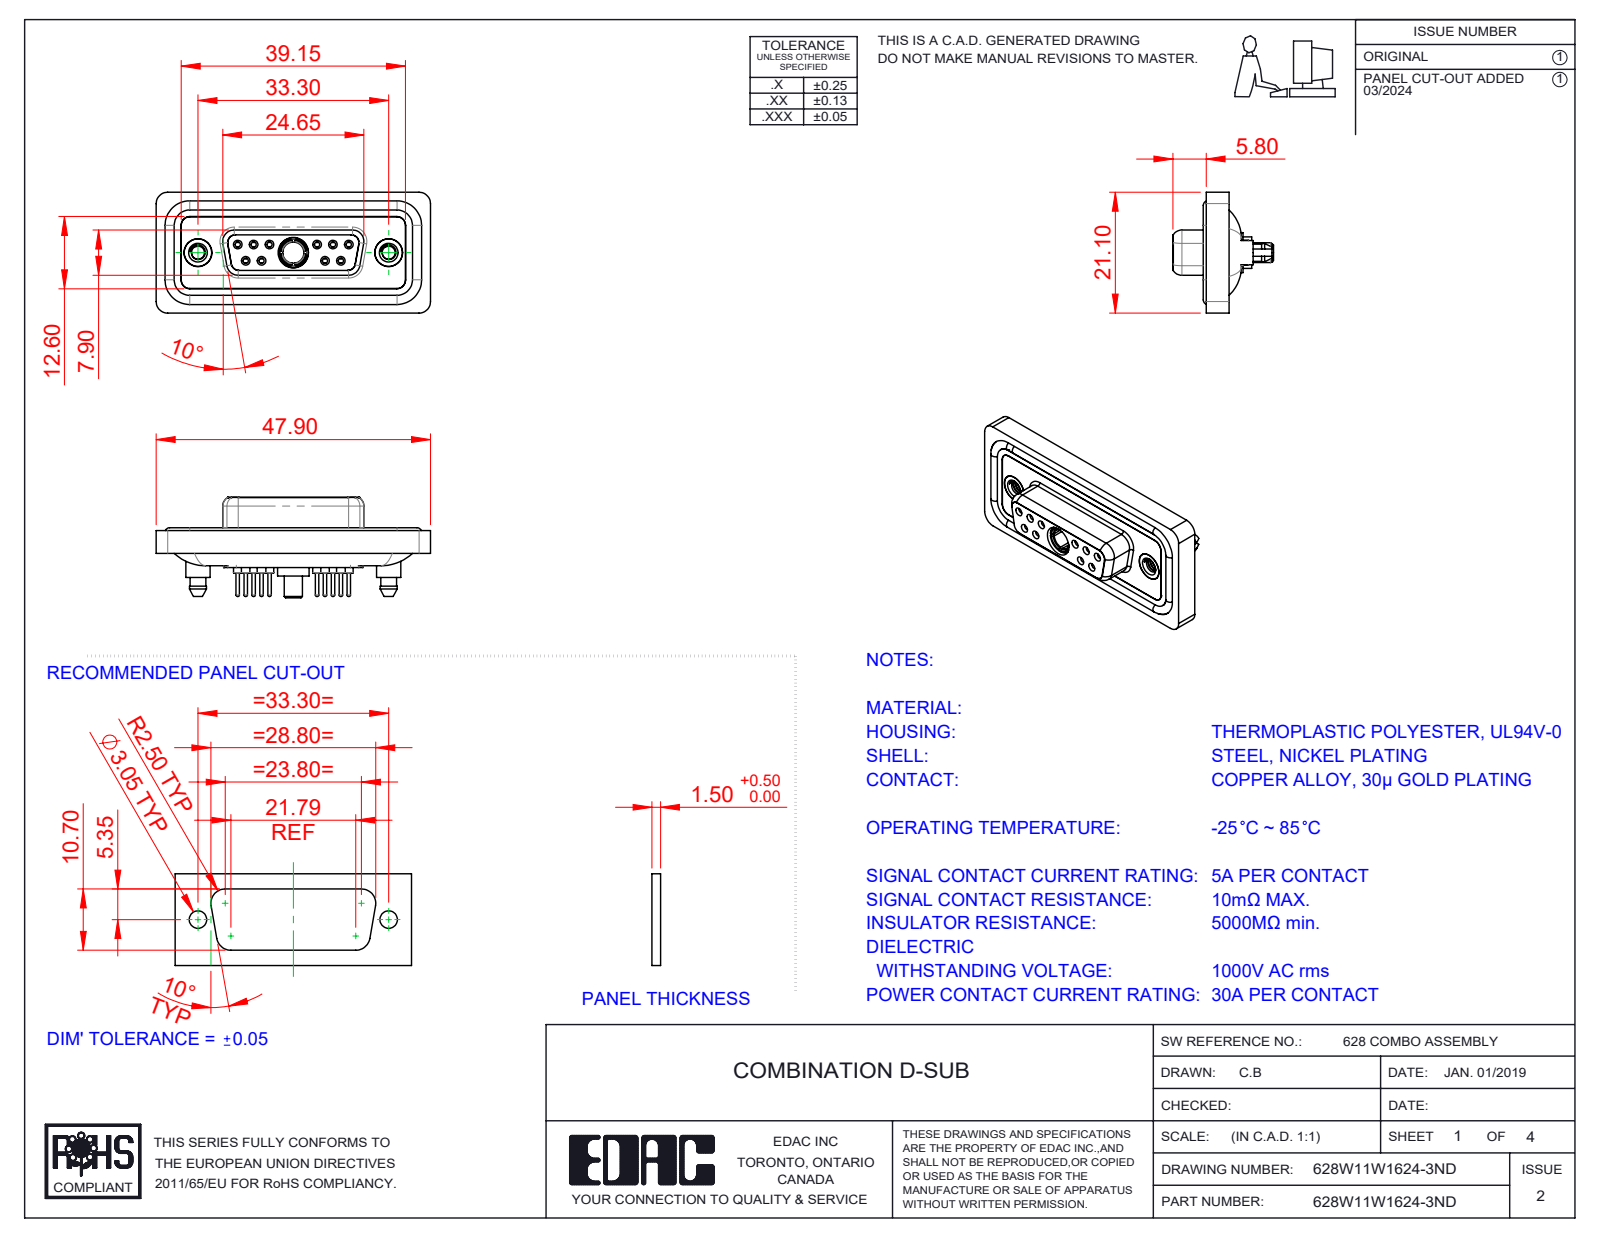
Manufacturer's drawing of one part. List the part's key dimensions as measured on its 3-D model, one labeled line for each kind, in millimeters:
Part name (STEP PRODUCT): 628Combo Contact Row 2_24; 628Combo Shell Front_15 Contacts; Power Socket_30A S; 628Combo Housing_11W1 (+5 more)
STEP written by: SolidWorks 2023 (CONFIG_CONTROL_DESIGN)
Units: millimetres
Bodies: 19 solids, 1076 faces (300 planar, 449 cylindrical, 327 other)
Overall size (bounding box): 47.9 × 21.1 × 17.55
Volume: 6 269 mm³ · Surface area: 10 376 mm²
Round holes (diameter × count): ⌀0.9 ×10, ⌀1.1 ×10, ⌀1.5 ×10, ⌀2 ×10, ⌀1.7 ×6, ⌀1.6 ×4, ⌀4.85 ×3, ⌀2.26 ×2, ⌀4 ×2, ⌀4.05 ×2, ⌀5 ×2, ⌀3.7 ×1
Round bosses / shafts (diameter × count): ⌀2.2 ×10, ⌀1.6 ×10, ⌀0.6 ×10, ⌀5.4 ×2, ⌀4.95 ×2, ⌀4.8 ×2, ⌀4.25 ×2, ⌀5.5 ×1
Partial cylindrical surfaces — rounded edges, fillets, slot ends (radius × count): R1.5 ×24, R2 ×20, R1.35 ×12, R1.6 ×10, R0.25 ×4, R0.5 ×4, R0.6 ×4, R0.65 ×4
Main face-to-face distances: 0.4, 1.6, 1.8, 2.9, 0.5, 1.1, 5.65, 7.45, 6.6, 7.05
Hole centre spacings: 3.16, 2.77, 13.85, 11.08, 16.62, 5.03, 5.04, 5.54
